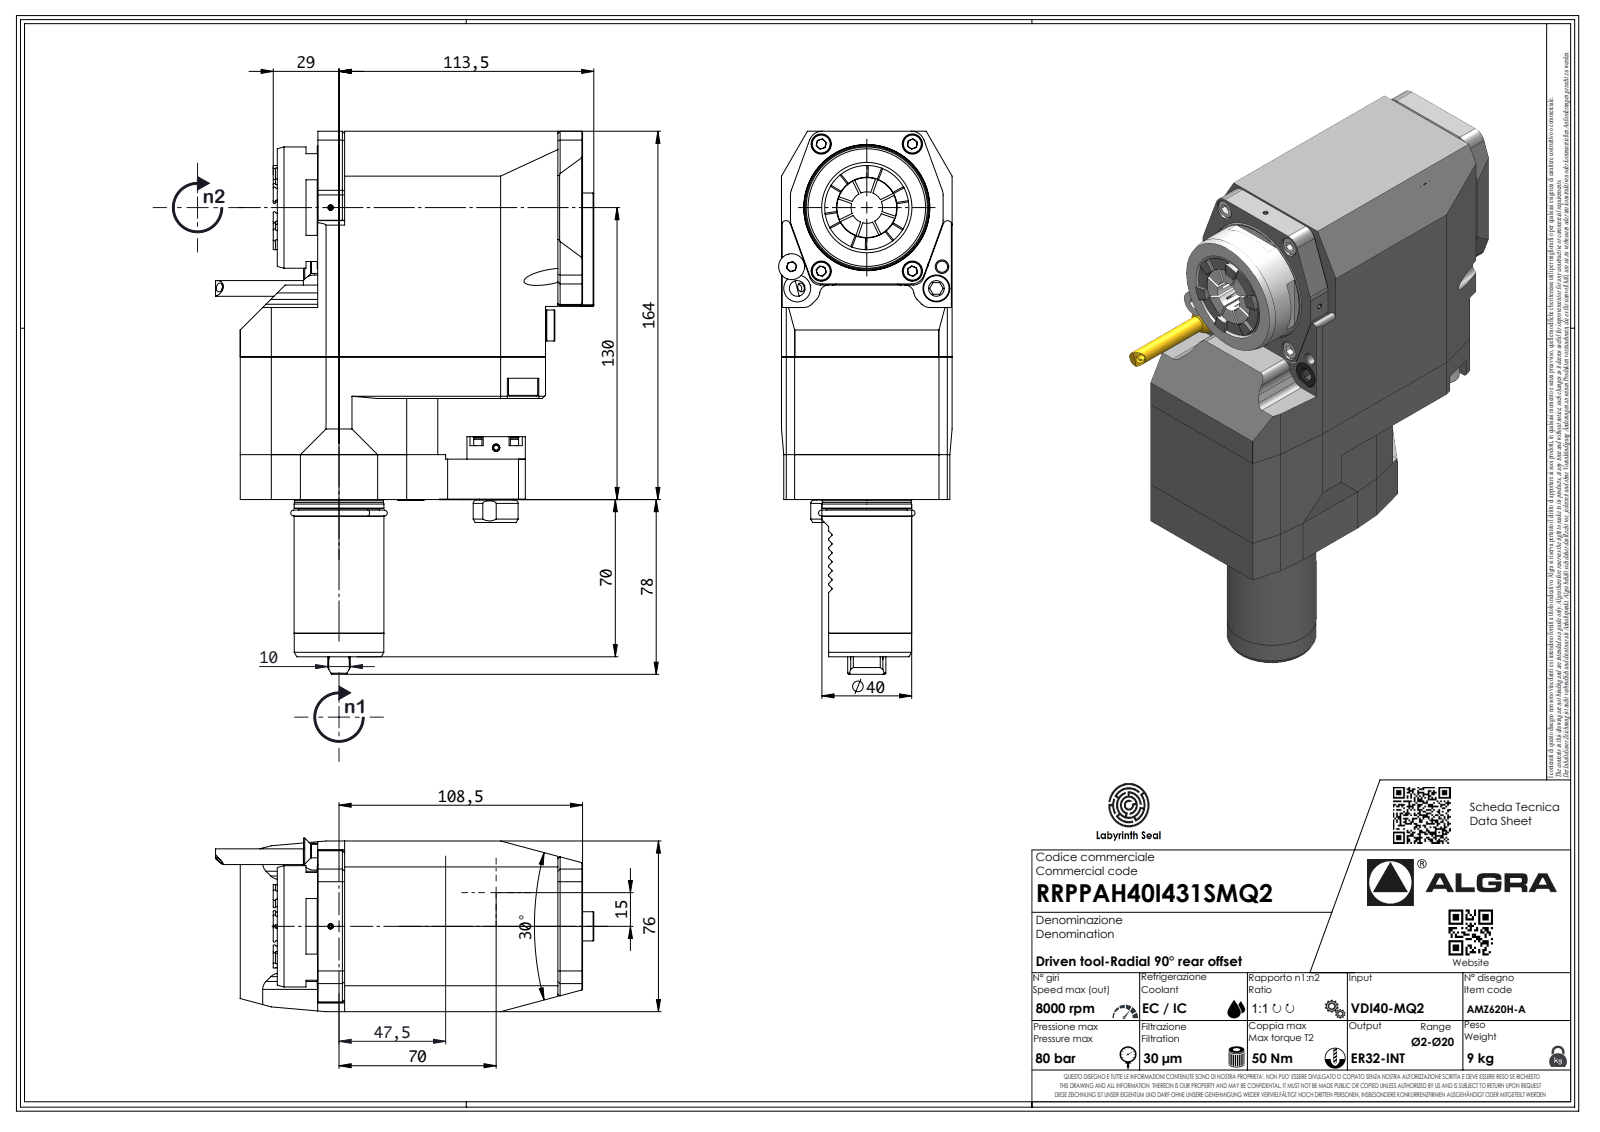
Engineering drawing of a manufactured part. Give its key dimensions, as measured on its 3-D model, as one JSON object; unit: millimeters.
{"part_name": "RRPPAH40I431SMQ2", "step_written_by": "SolidWorks 2023 (AUTOMOTIVE_DESIGN)", "units": "millimeters", "bodies": {"solids": 2, "faces": 690, "planar": 419, "cylindrical": 124, "other": 147}, "overall_size": [241.8, 168.5, 76], "volume_mm3": 1508000, "surface_area_mm2": 103201, "round_holes": [[2.1, 1], [4, 1]], "round_bosses_or_shafts": [[54, 1], [40, 1], [39.9, 1], [39.6, 1], [36, 1], [26, 1], [20, 1], [15, 1]], "partial_cylinders_radius": [[6, 10], [1, 8], [3, 8], [0.3, 7], [0.33, 7], [0.52, 7], [3.7, 7], [5, 6]], "face_to_face_distances": [76, 164, 136, 16.5, 45, 119, 152.5, 88, 119.5, 68.5]}
